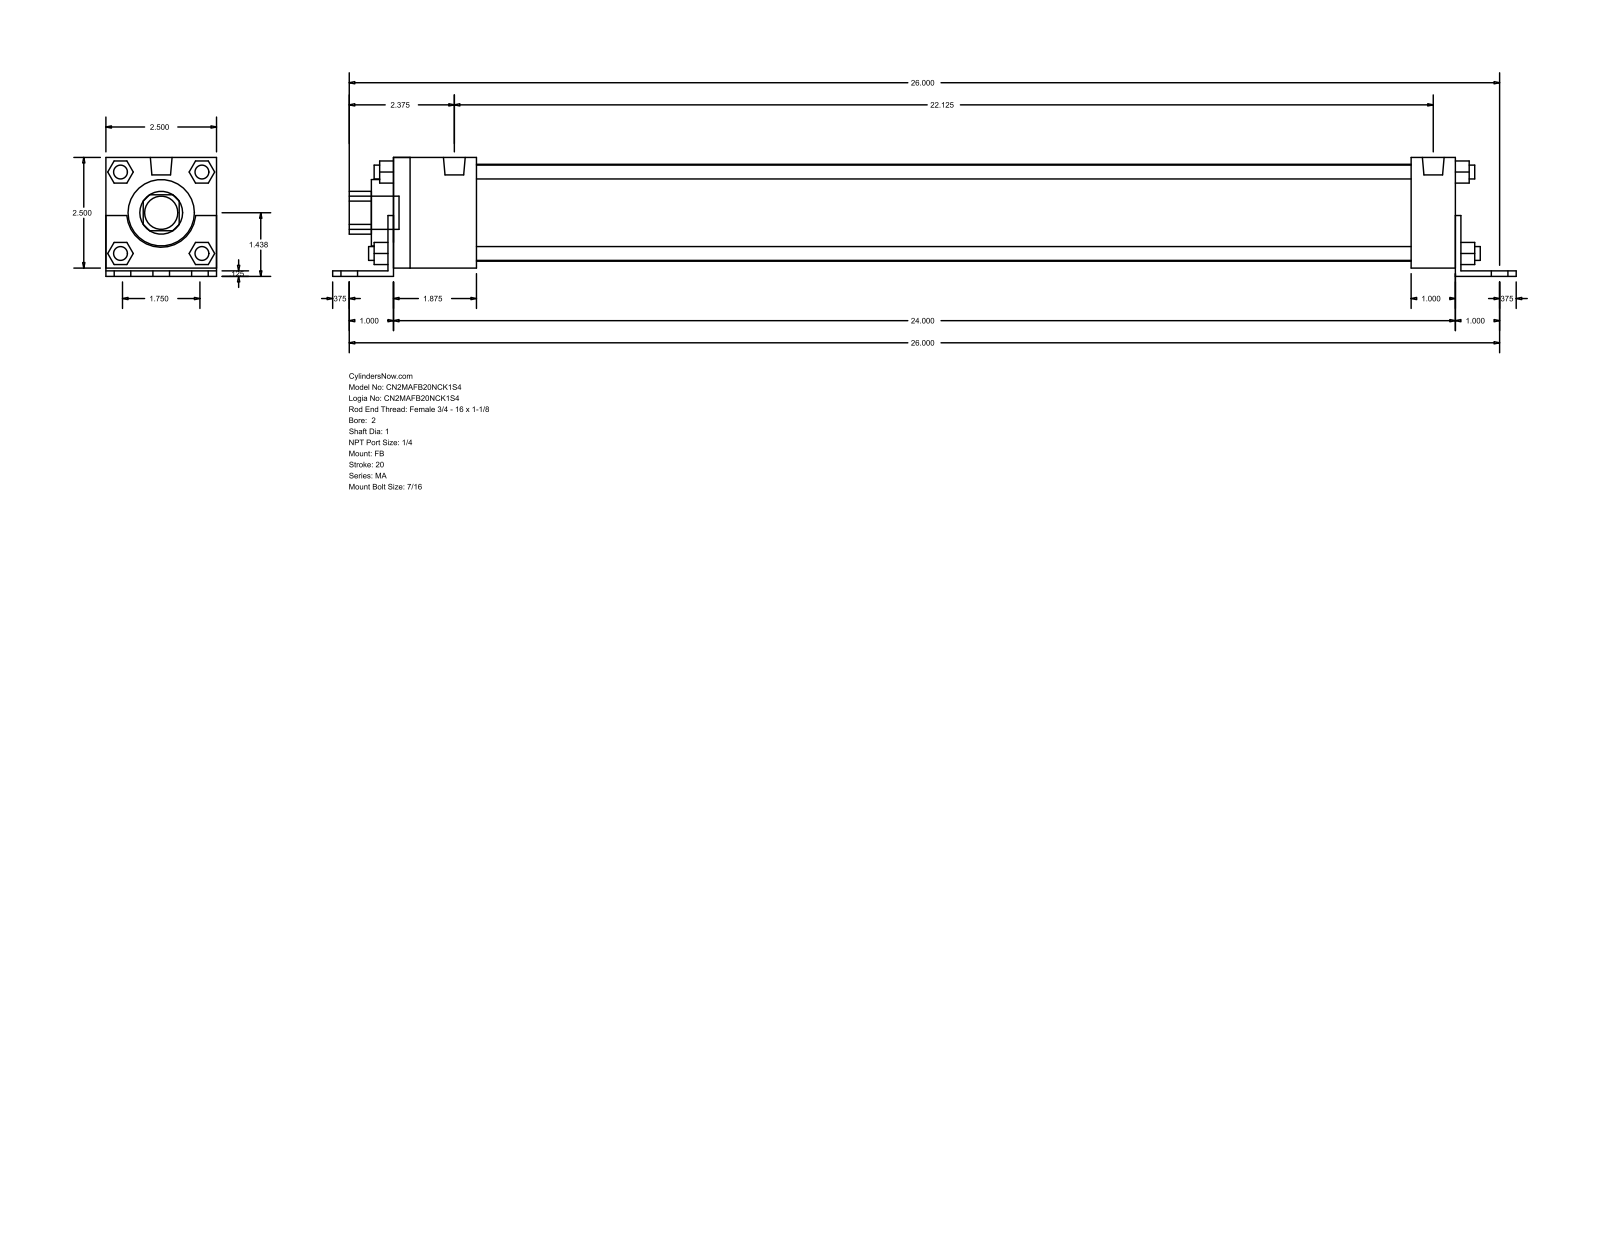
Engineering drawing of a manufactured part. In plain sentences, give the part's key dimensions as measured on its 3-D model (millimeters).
The part is named "MA_FB__0200_1". Its 3-D file was written by "GSSL Pune (CONFIG_CONTROL_DESIGN)". It is 0 solids with 140 faces: 105 planar, 35 cylindrical and 0 other. Overall it measures 679.45 by 68.26 by 63.5 millimeters. Round holes: 1 of diameter 25.4, 1 of diameter 38.1, 1 of diameter 55.63. Round bosses or shafts: 8 of diameter 7.94, 6 of diameter 11.11, 2 of diameter 12.49, 1 of diameter 19.05. Partial cylindrical surfaces (rounded edges, fillets, slot ends): 1 of radius 12.29, 1 of radius 19.81. The main face-to-face distances are 63.5, 3.17, 4.76, 68.26, 1.59, 65.09, 612.77, 12.7, 609.6, 25.4.
